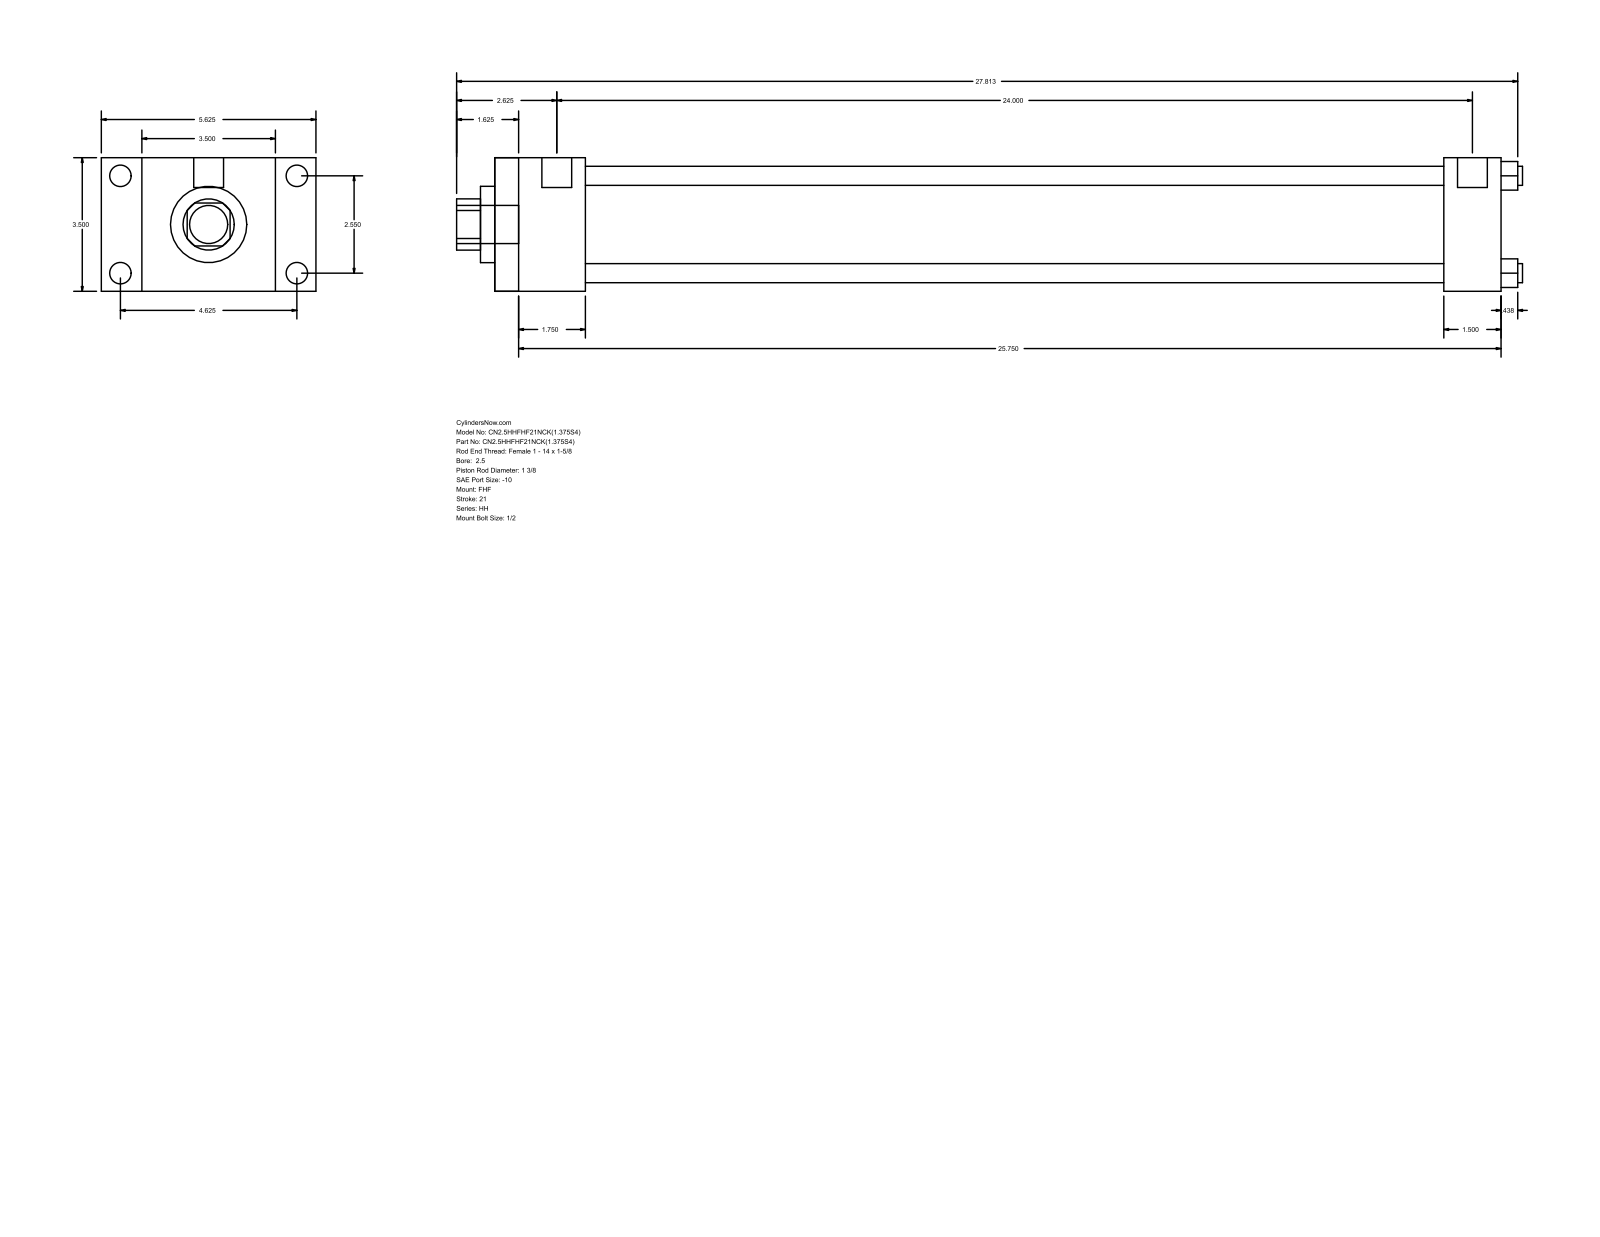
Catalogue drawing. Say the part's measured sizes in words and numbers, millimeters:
The part is named "HH_FHF__0250_1.375". Its 3-D file was written by "GSSL Pune (CONFIG_CONTROL_DESIGN)". It is 0 solids with 88 faces: 60 planar, 28 cylindrical and 0 other. Overall it measures 709.61 by 142.88 by 88.9 millimeters. Round holes: 4 of diameter 12.7, 1 of diameter 34.92, 1 of diameter 50.8, 1 of diameter 73.03. Round bosses or shafts: 4 of diameter 14.3, 4 of diameter 5.56, 2 of diameter 19.84, 1 of diameter 25.4. Partial cylindrical surfaces (rounded edges, fillets, slot ends): 1 of radius 17.06. The main face-to-face distances are 88.9, 60.32, 26.99, 115.89, 669.93, 609.61, 142.88, 631.83, 571.51, 38.1. The hole center spacings are 45.79, 64.76, 91.58.
